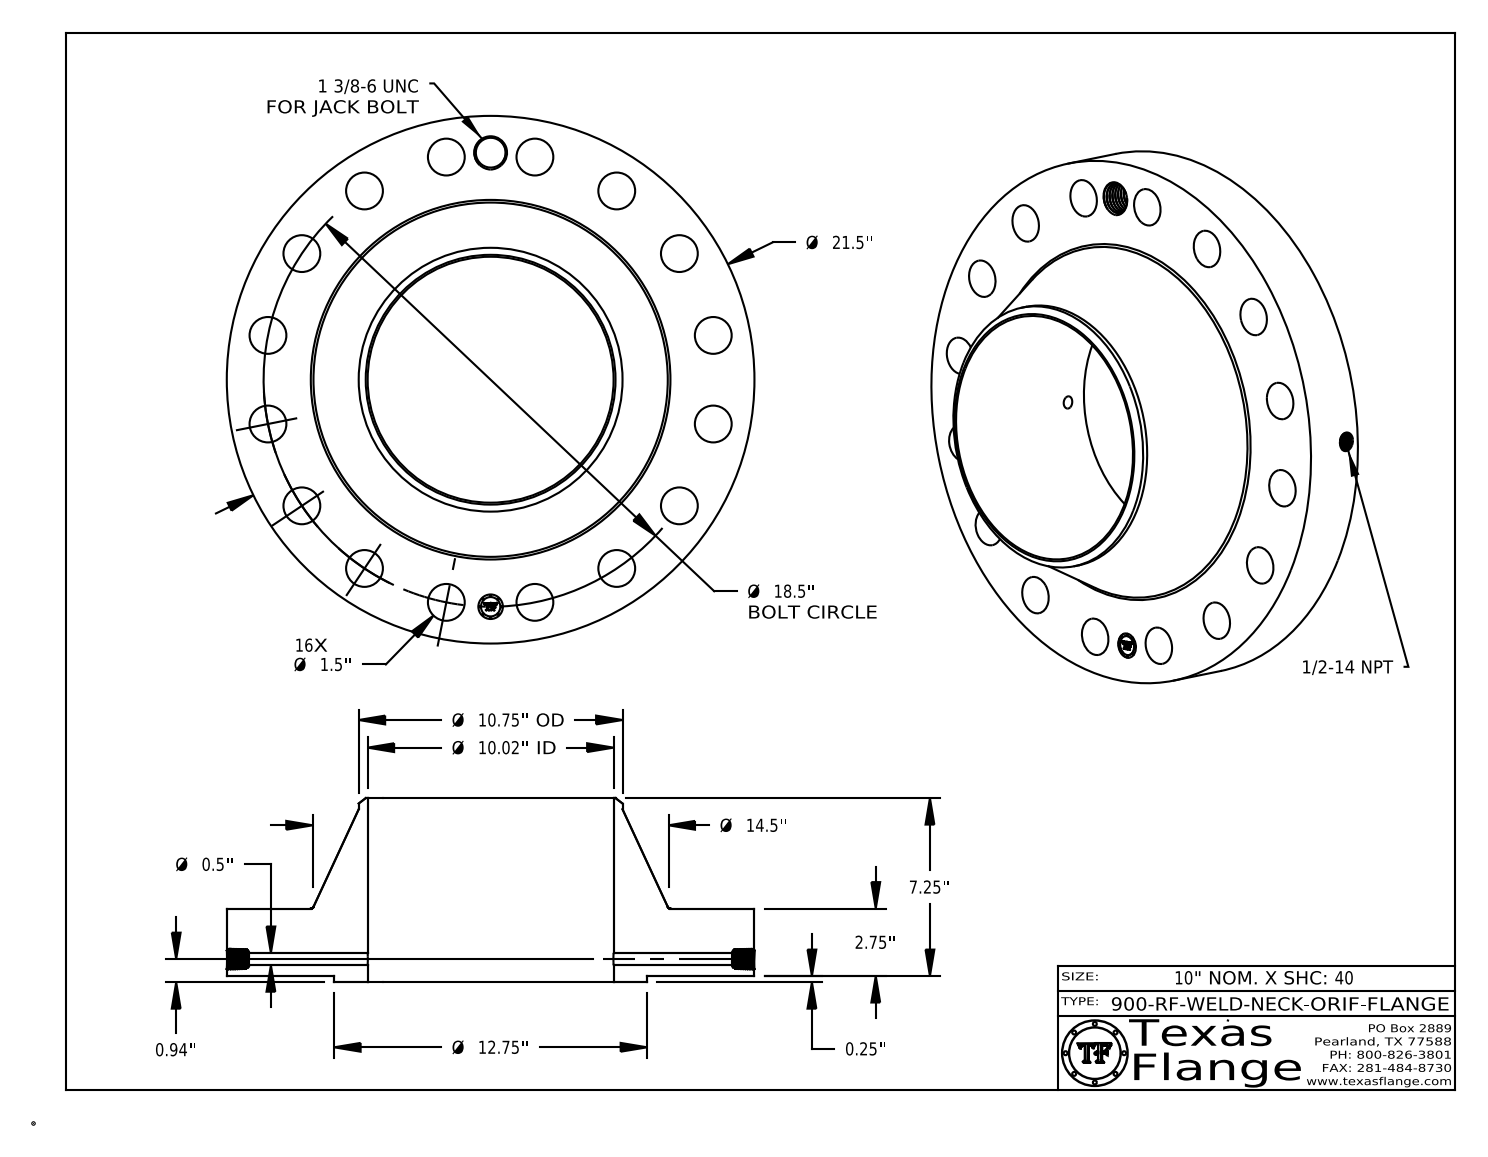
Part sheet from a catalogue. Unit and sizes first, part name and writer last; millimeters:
Units: millimetres
Overall size (bounding box): 546.1 × 546.1 × 190.5
Round holes (diameter × count): ⌀38.1 ×16, ⌀12.7 ×1, ⌀17.1 ×1, ⌀25.4 ×1, ⌀31 ×1, ⌀254.5 ×1
Round bosses / shafts (diameter × count): ⌀1.5 ×8, ⌀546.1 ×1, ⌀323.9 ×1, ⌀273.1 ×1, ⌀20 ×1
Main face-to-face distances: 69.9, 6.4, 76.2, 190.5, 184.2, 114.3, 75.8, 69.5, 0.4, 114.7
Hole centre spacings: 261.1, 434.1, 91.7, 235, 179.8, 179.8, 235, 332.3
Volume: 14 830 000 mm³ · Surface area: 836 800 mm²
Bodies: 1 solid, 794 faces (369 planar, 113 cylindrical, 312 other)
Part name (STEP PRODUCT): 900-RF-WELD-NECK
STEP written by: CATIA V5 STEP AP214 (AUTOMOTIVE_DESIGN)
